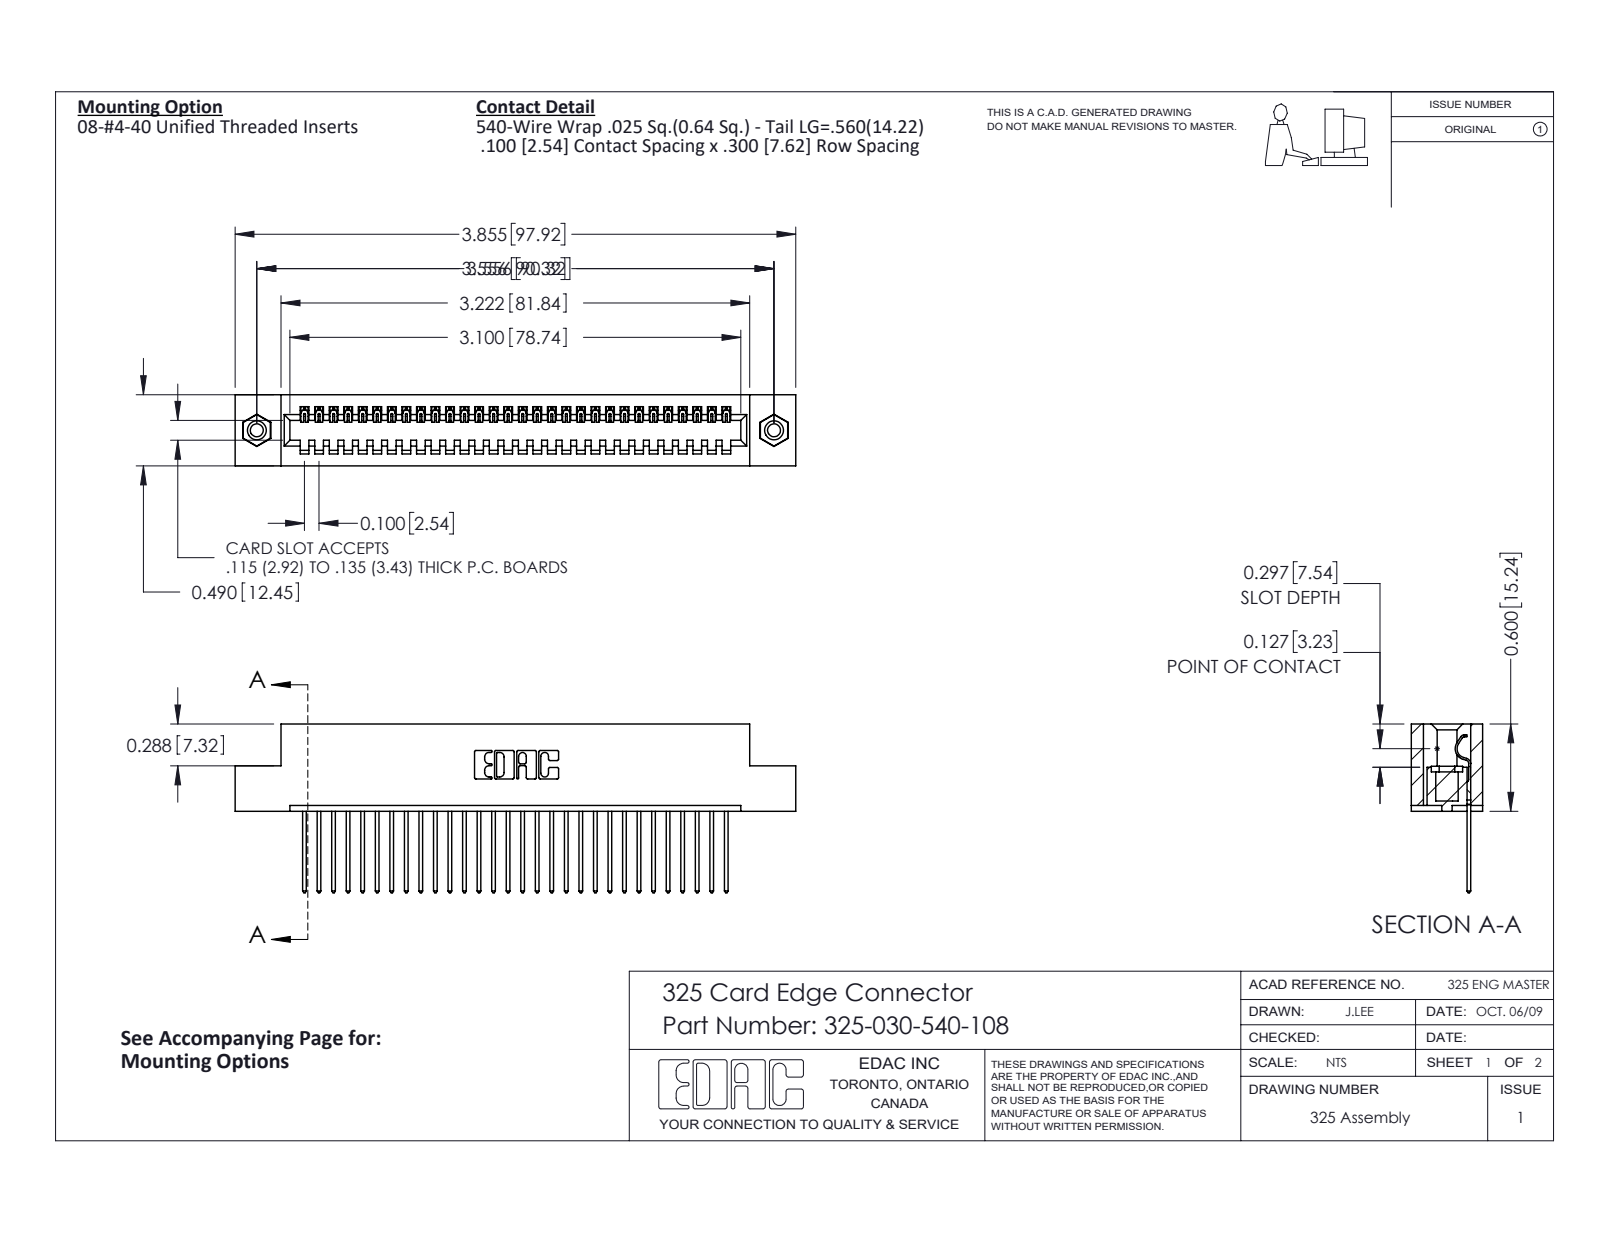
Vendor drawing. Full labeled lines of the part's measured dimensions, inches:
Part name (STEP PRODUCT): 325-030-540-108; 325 Part_TI; 345-250-001_345-250-003-102; 325-292-001_325-293-140
STEP written by: SolidWorks 2016 (CONFIG_CONTROL_DESIGN)
Units: inches
Bodies: 33 solids, 1914 faces (1362 planar, 536 cylindrical, 16 other)
Overall size (bounding box): 3.855 × 1.16 × 0.49
Volume: 0.755 in³ · Surface area: 21.12 in²
Round holes (diameter × count): ⌀0.089 ×2, ⌀0.125 ×2, ⌀0.16 ×2
Round bosses / shafts (diameter × count): ⌀0.155 ×2
Partial cylindrical surfaces — rounded edges, fillets, slot ends (radius × count): R0.006 ×60, R0.01 ×60, R0.01 ×22, R0.007 ×6, R0.031 ×6, R0.026 ×3, R0.014 ×1, R0.022 ×1
Main face-to-face distances: 0.083, 0.407, 0.49, 0.3, 0.107, 0.383, 0.025, 0.325, 0.04, 0.56
Hole centre spacings: 3.556
